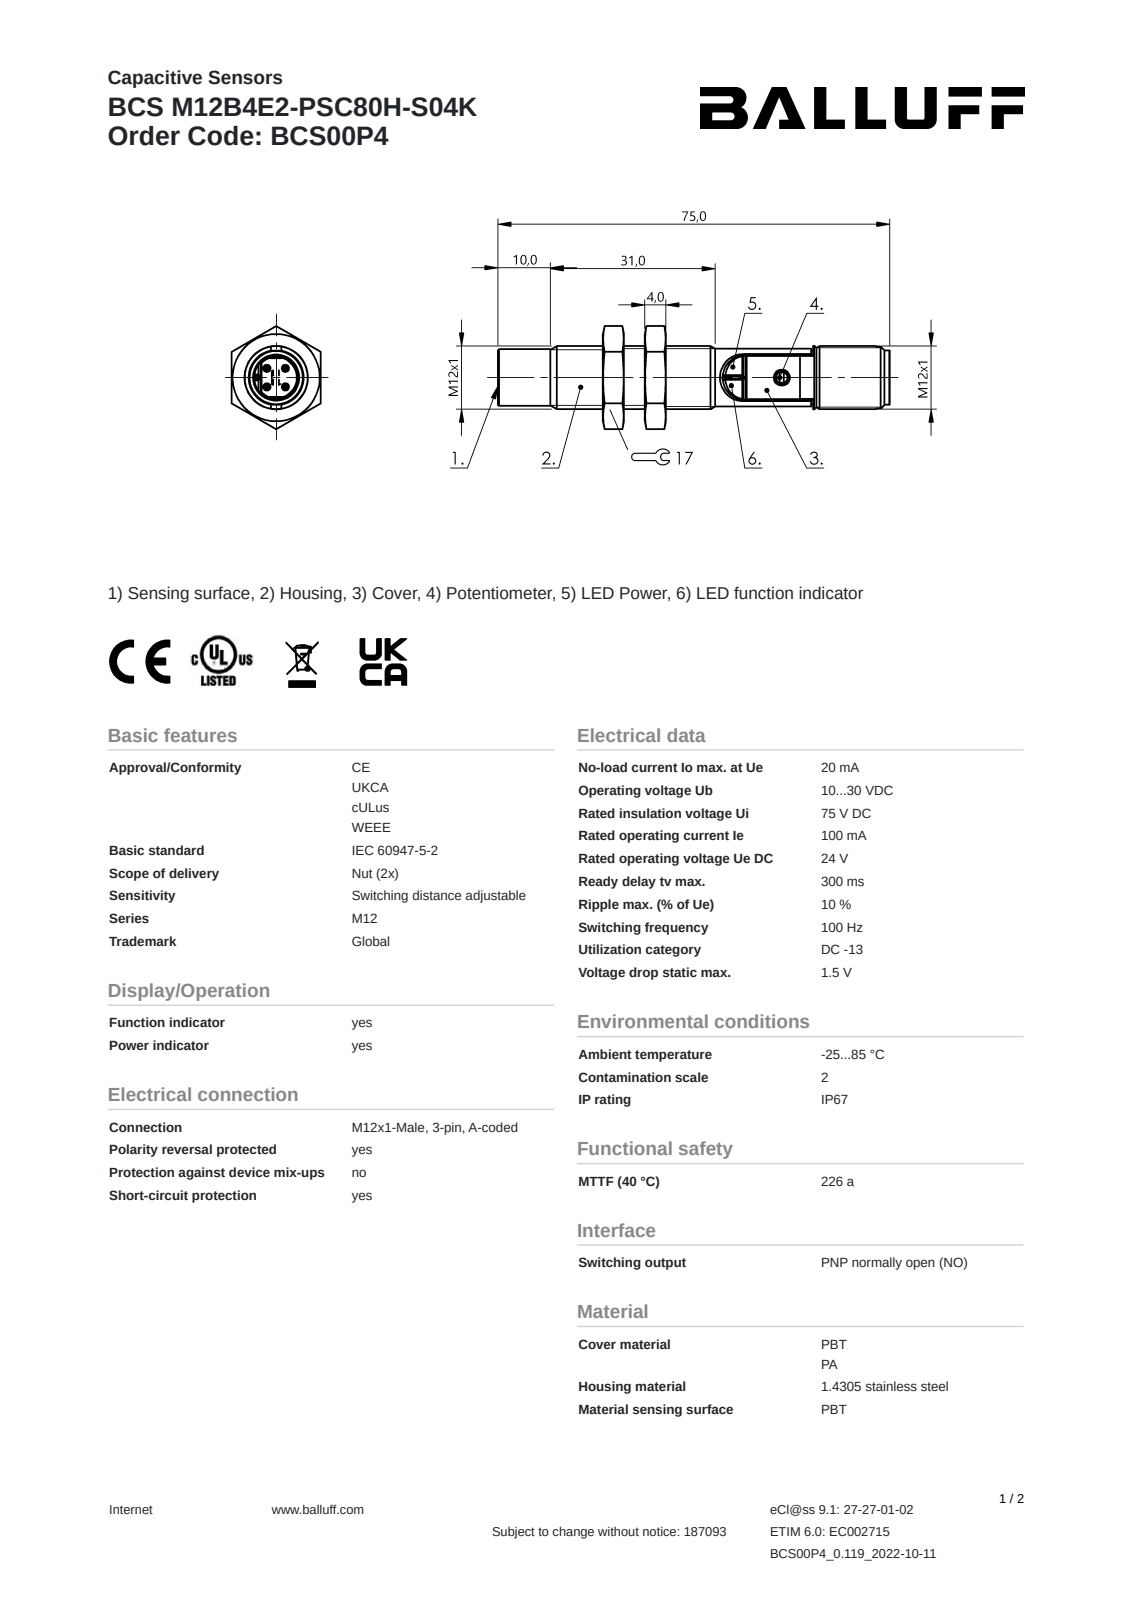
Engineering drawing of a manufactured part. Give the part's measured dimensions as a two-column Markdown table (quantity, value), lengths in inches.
| quantity | value |
| --- | --- |
| part name | BCS00P4 |
| STEP written by | SolidWorks 2021 (AUTOMOTIVE_DESIGN) |
| units | inches |
| bodies | 3 solids, 180 faces (86 planar, 49 cylindrical, 45 other) |
| overall size | 2.953 × 0.773 × 0.669 |
| volume | 0.513 in³ |
| surface area | 7.378 in² |
| round holes (diameter × count) | 0.135 × 1, 0.331 × 1, 0.43 × 1 |
| round bosses / shafts (diameter × count) | 0.039 × 4, 0.472 × 1, 0.467 × 1, 0.423 × 1, 0.407 × 1, 0.406 × 1 |
| partial cylindrical surfaces (radius × count) | 0.004 × 8, 0.006 × 2, 0.009 × 2, 0.01 × 1, 0.024 × 1, 0.061 × 1, 0.156 × 1, 0.157 × 1 |
| main face-to-face distances | 0.276, 0.157, 0.669, 0.433, 0.118, 1.043, 0.886, 0.768, 0.61, 1.563 |
